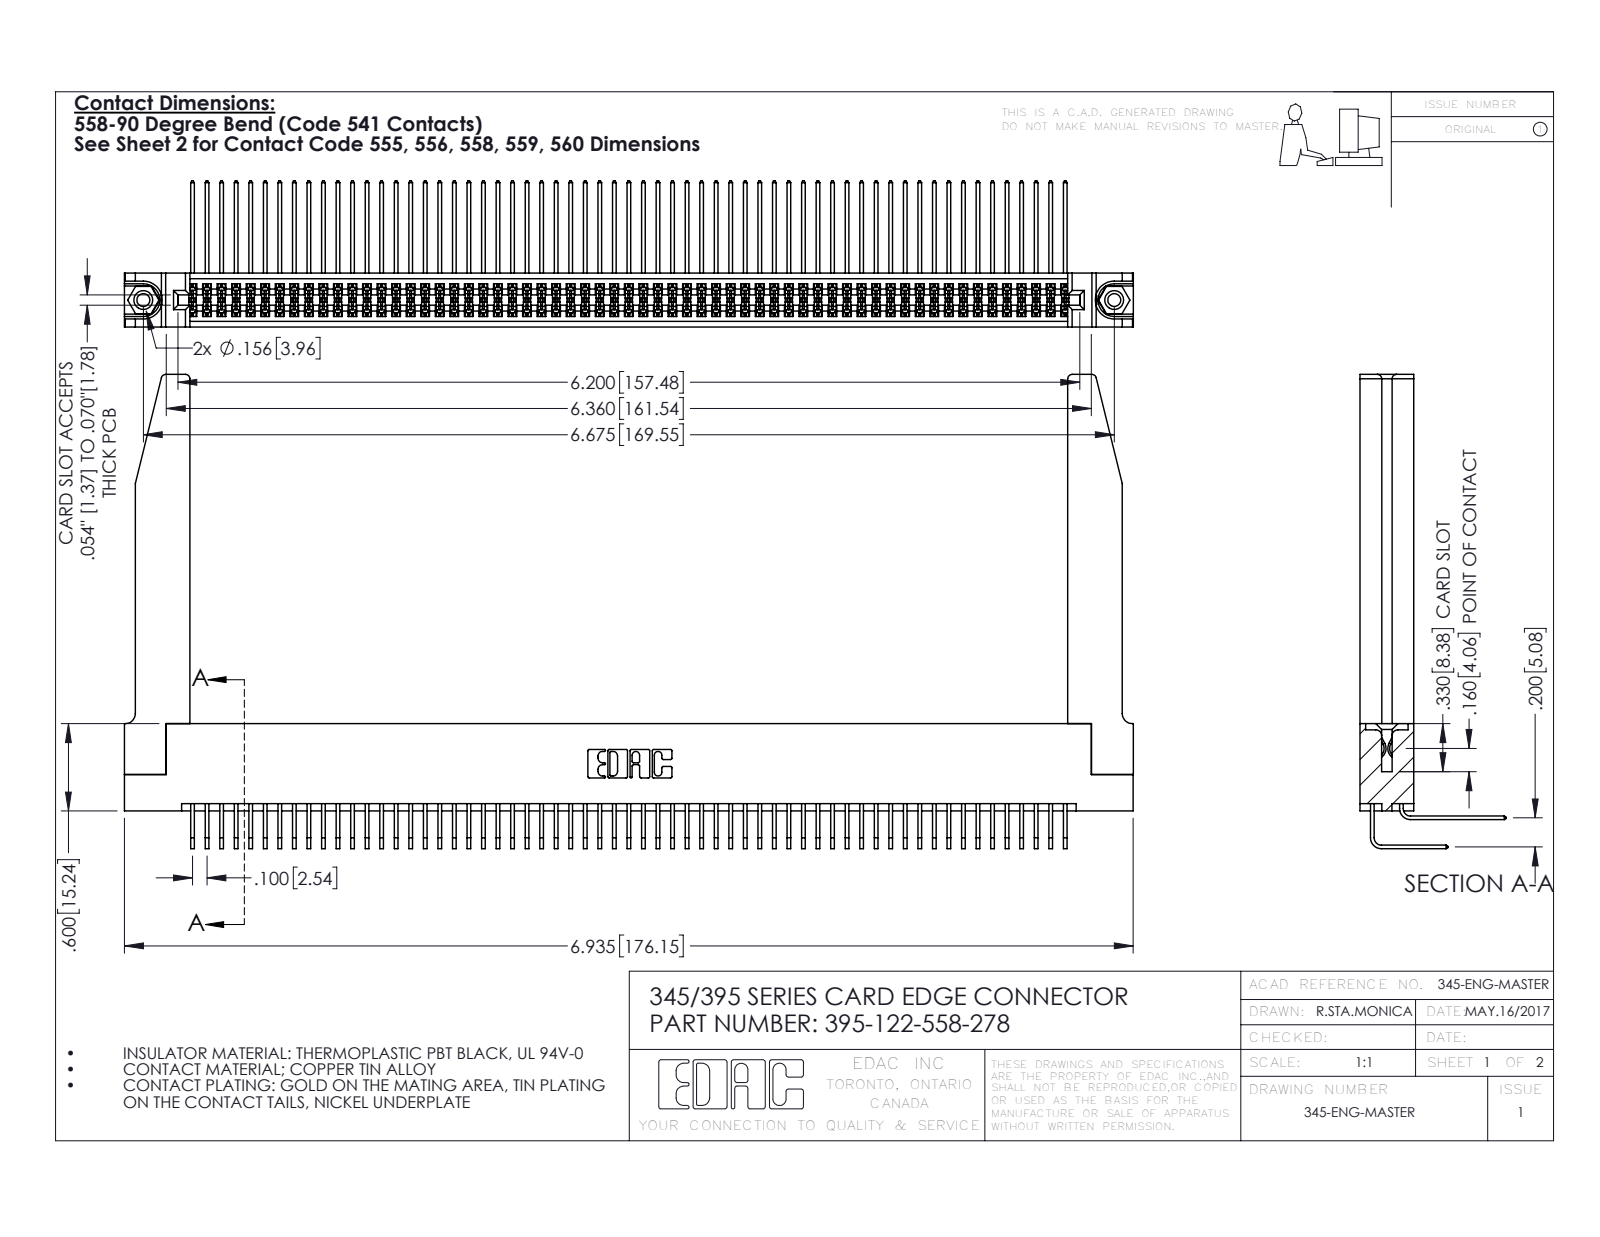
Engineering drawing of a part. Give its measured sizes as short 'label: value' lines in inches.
name: 345 Part_Flush Mounting Lugs - 0.156 Dia-TH; 345-292-001_558 559 Tail - 1; 345-220-078_345-220-078; 345-292-001_558 Tail - 2 (+2 more)
written by: SolidWorks 2016 (CONFIG_CONTROL_DESIGN)
unit: in
bodies: 127 solids, 6704 faces (4492 planar, 2160 cylindrical, 52 other)
size: 6.936 × 3.259 × 1.005
volume: 1.572 in³; area: 57.53 in²
holes: 2× ⌀0.089, 2× ⌀0.125, 2× ⌀0.156, 1× ⌀0.064
bosses: 2× ⌀0.155
rounds: 184× R0.006, 22× R0.01, 8× R0.03, 6× R0.007, 6× R0.031, 3× R0.026, 2× R0.014, 2× R0.019
face distances: 0.072, 0.298, 0.37, 0.2, 0.098, 0.272, 0.025, 0.225, 0.025, 0.285
hole spacings: 0.27, 6.439, 6.675
